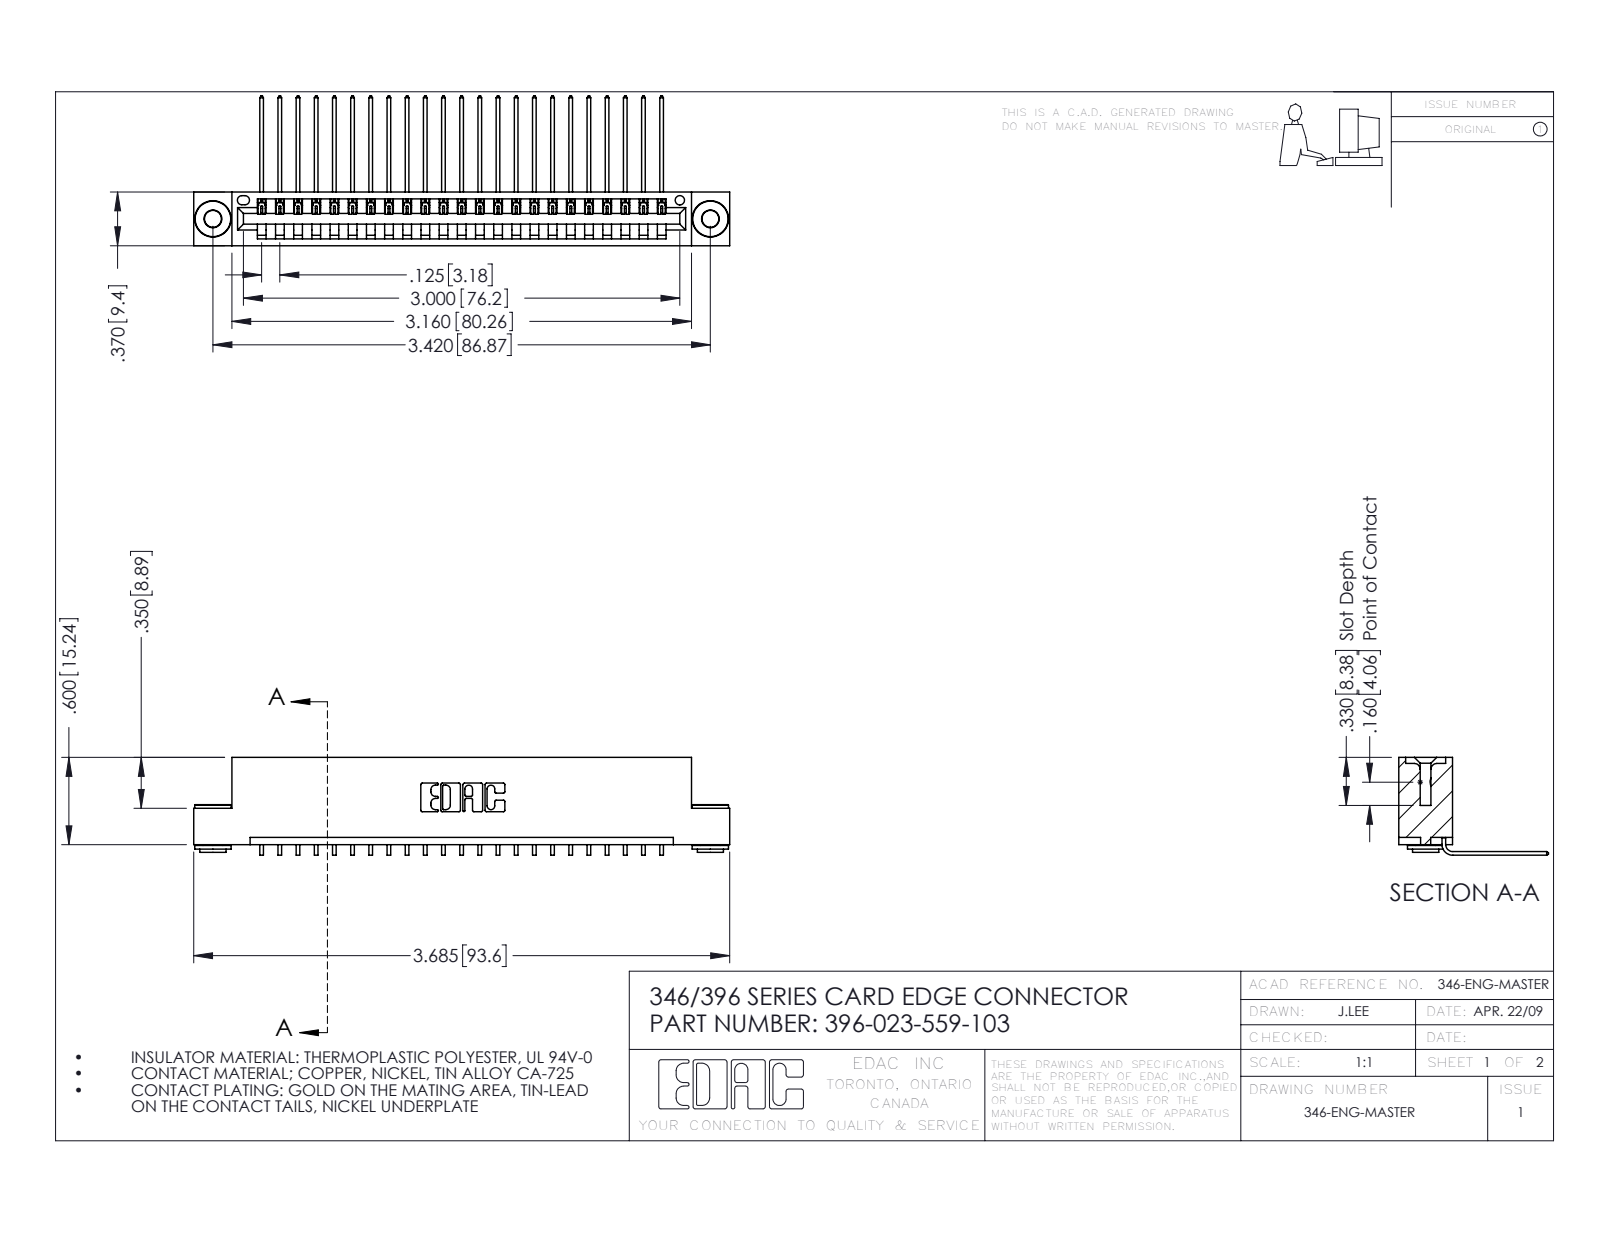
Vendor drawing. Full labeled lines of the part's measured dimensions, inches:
Part name (STEP PRODUCT): 346 Part_Flush Mounting Lugs - 0.156 Dia-TH; 396-023-559-103; 345-292-001_558 559 Tail - 1; 345-250-002_345-250-002-102
STEP written by: SolidWorks 2016 (CONFIG_CONTROL_DESIGN)
Units: inches
Bodies: 26 solids, 1540 faces (1052 planar, 480 cylindrical, 8 other)
Overall size (bounding box): 3.685 × 1.03 × 0.673
Volume: 0.545 in³ · Surface area: 18.02 in²
Round holes (diameter × count): ⌀0.116 ×2, ⌀0.156 ×2, ⌀0.064 ×1
Round bosses / shafts (diameter × count): ⌀0.25 ×2, ⌀0.18 ×2, ⌀0.136 ×2
Partial cylindrical surfaces — rounded edges, fillets, slot ends (radius × count): R0.006 ×46, R0.01 ×22, R0.007 ×6, R0.031 ×6, R0.026 ×3, R0.031 ×2, R0.04 ×2, R0.014 ×1
Main face-to-face distances: 0.048, 0.322, 0.25, 0.37, 0.025, 0.072, 0.298, 0.148, 0.222, 0.1
Hole centre spacings: 0.246, 3.212, 3.42
